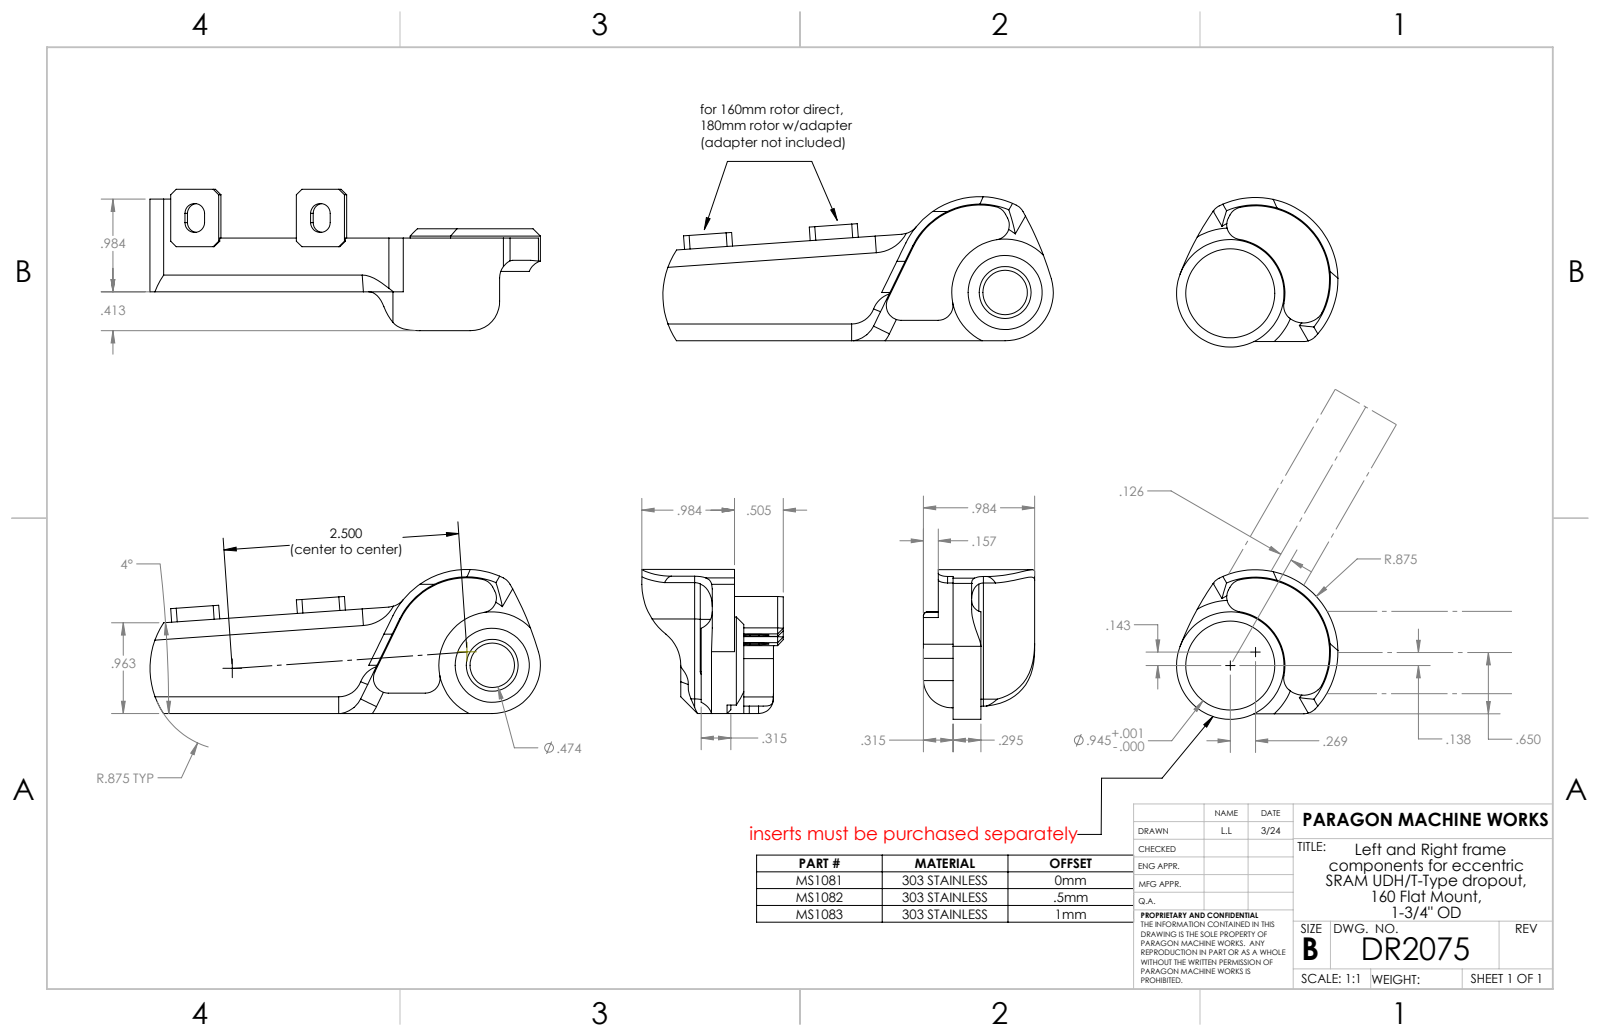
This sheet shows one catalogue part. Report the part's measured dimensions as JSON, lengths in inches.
{"part_name": "DR2077_no toobs; DR2075; DR2073R_DR2073R", "step_written_by": "SolidWorks 2023 (AUTOMOTIVE_DESIGN)", "units": "inches", "bodies": {"solids": 2, "faces": 208, "planar": 95, "cylindrical": 91, "other": 22}, "overall_size": [7.48, 4.207, 1.589], "volume_in3": 1.703, "surface_area_in2": 32.43, "round_holes": [[0.472, 1], [0.945, 1]], "partial_cylinders_radius": [[0.157, 26], [0.138, 5], [0.104, 4], [0.315, 3], [0.039, 2], [0.165, 2], [0.187, 2], [0.098, 1]], "face_to_face_distances": [0.079, 0.492, 6.398, 5.906, 0.571, 0.413, 6.319, 5.827, 6.476, 0.039]}
